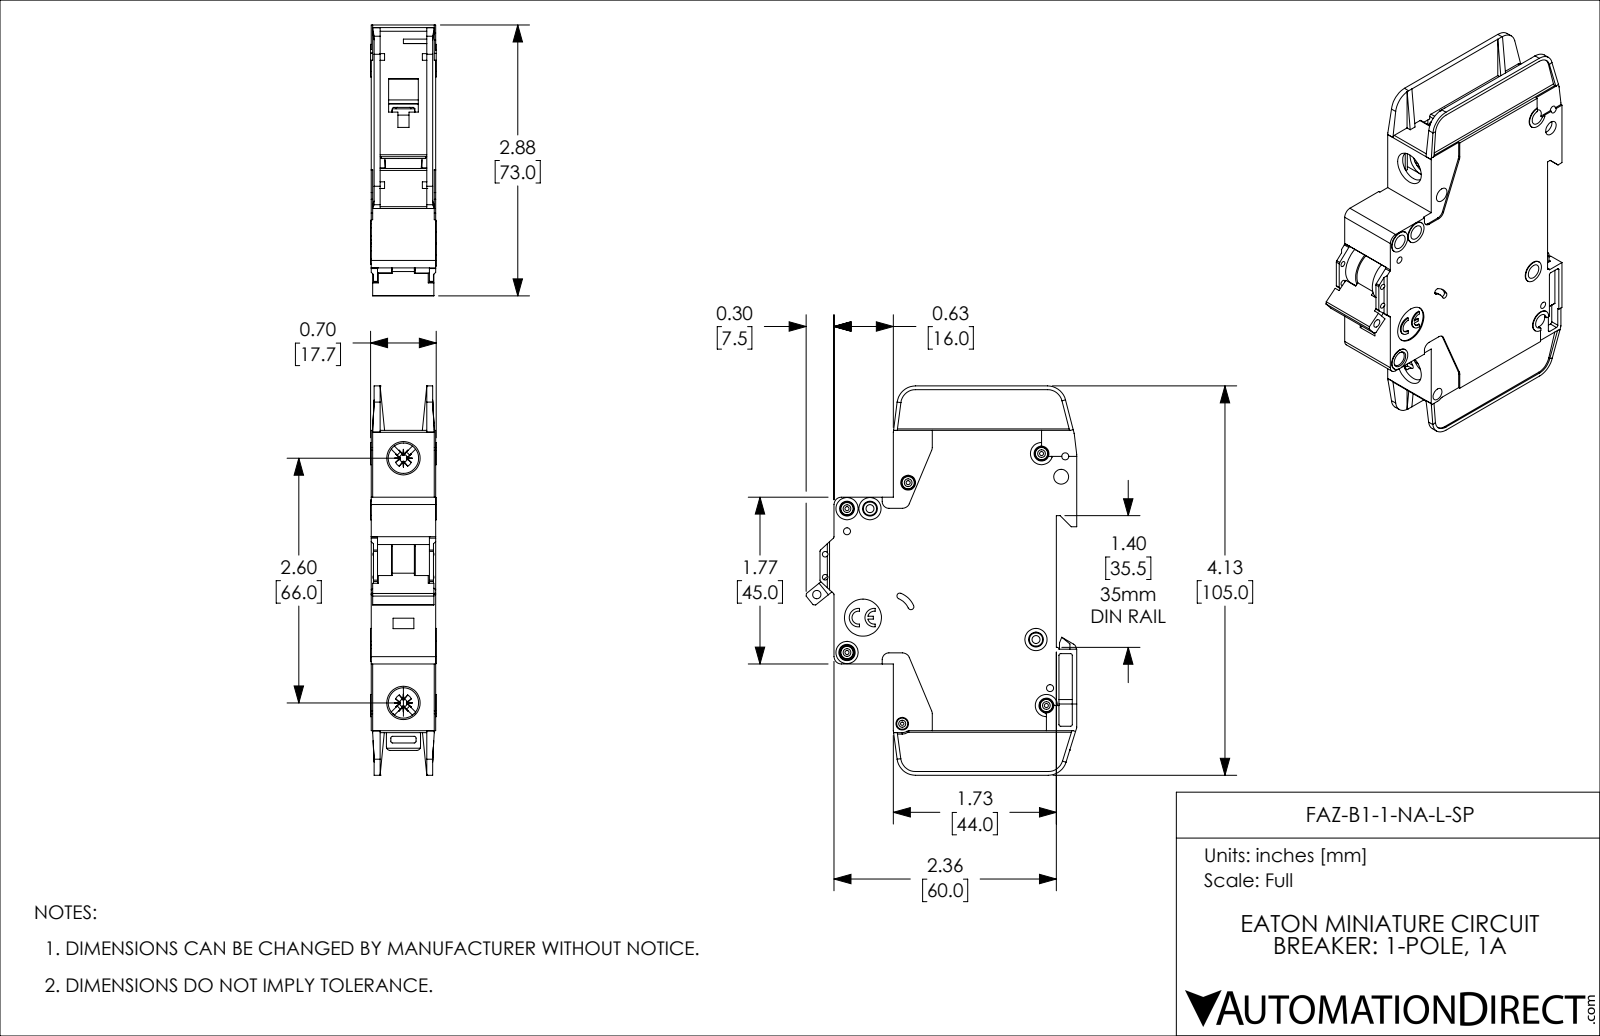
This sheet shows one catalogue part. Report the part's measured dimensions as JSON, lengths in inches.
{"part_name": "FAZ-B1-1-NA-L-SP", "step_written_by": "SolidWorks 2019 (AUTOMOTIVE_DESIGN)", "units": "inches", "bodies": {"solids": 1, "faces": 1127, "planar": 671, "cylindrical": 357, "other": 99}, "overall_size": [4.134, 2.876, 0.697], "volume_in3": 4.682, "surface_area_in2": 41.01, "round_holes": [[0.157, 8], [0.043, 5], [0.075, 4], [0.059, 2], [0.085, 2], [0.323, 2], [0.035, 1], [0.089, 1], [0.098, 1], [0.134, 1], [0.394, 1]], "round_bosses_or_shafts": [[0.13, 5], [0.236, 4], [0.118, 2], [0.098, 1]], "partial_cylinders_radius": [[0.02, 42], [0.016, 10], [0.039, 10], [0.079, 8], [0.197, 5], [0.008, 4], [0.026, 4], [0.043, 4]], "face_to_face_distances": [0.047, 0.685, 0.591, 0.638, 0.094, 0.543, 0.016, 0.031, 0.496, 0.575], "hole_center_spacings": [0.244, 0.537, 0.87, 0.189, 0.199, 0.204, 0.221, 0.24]}
